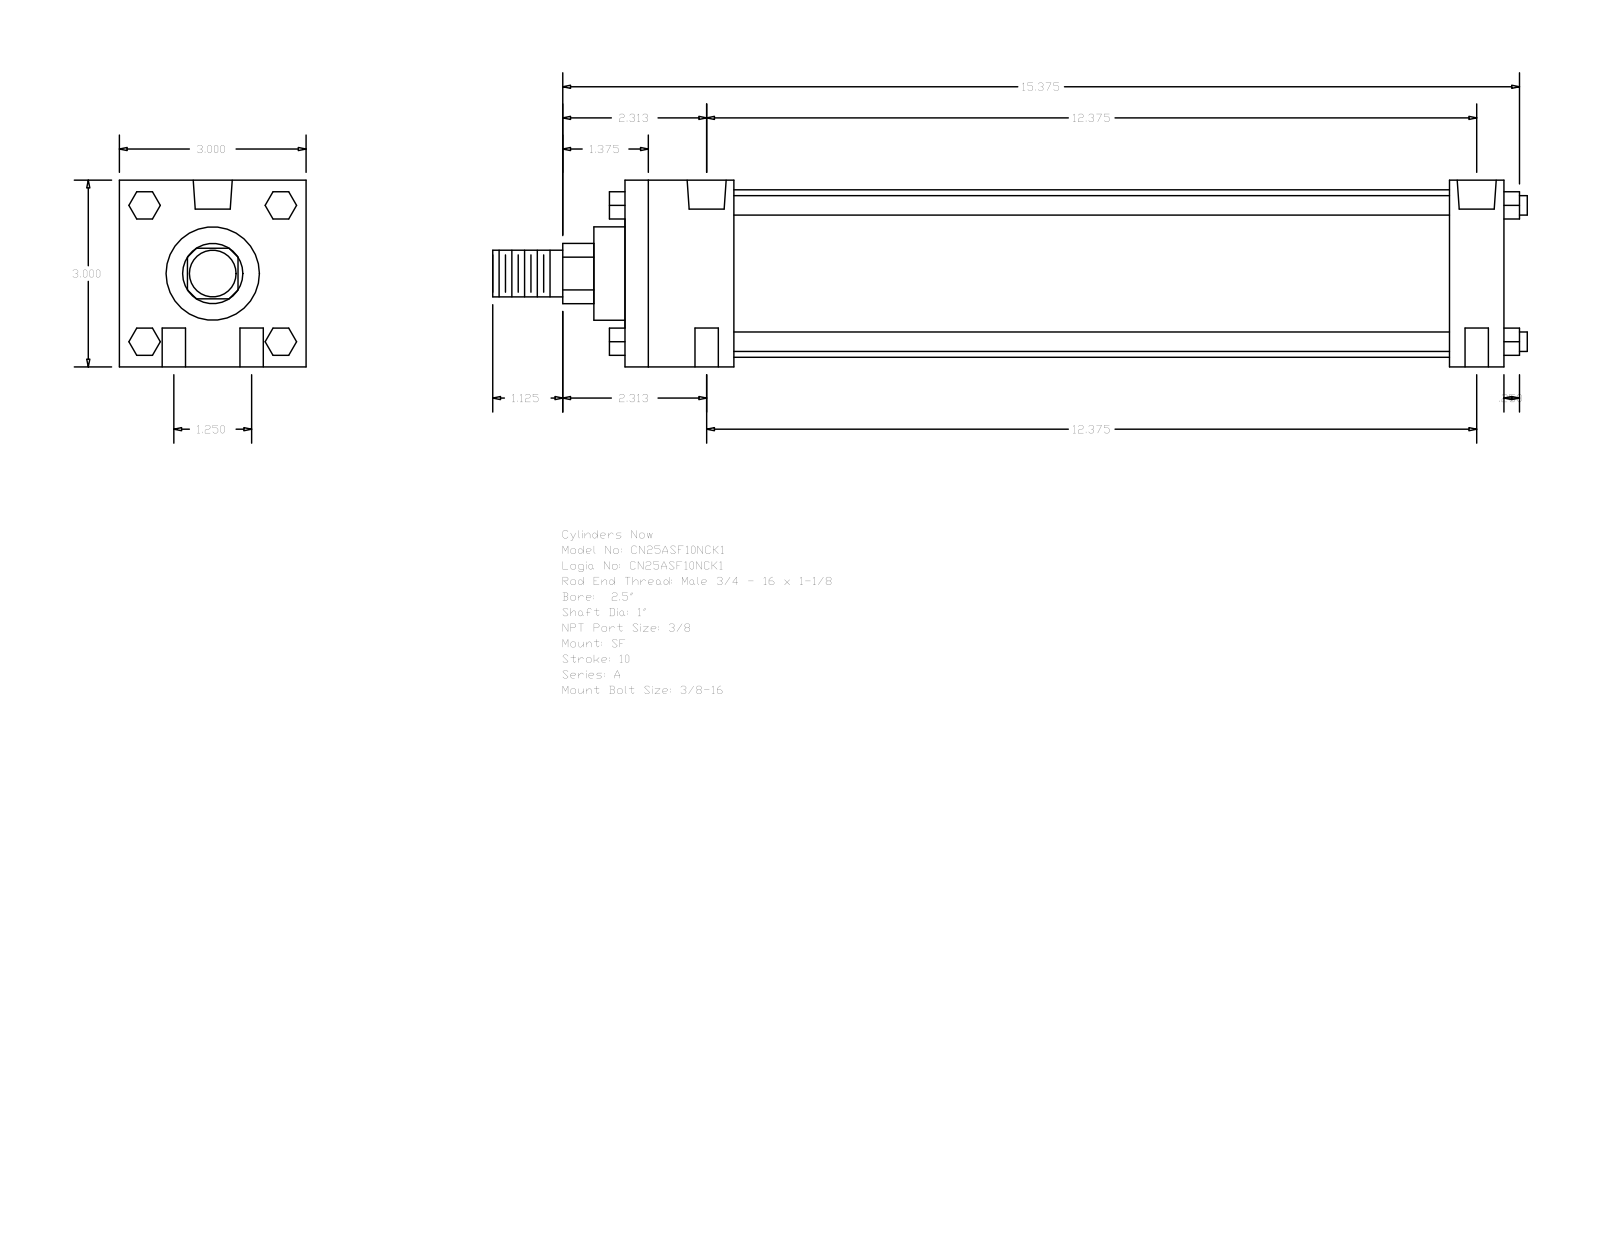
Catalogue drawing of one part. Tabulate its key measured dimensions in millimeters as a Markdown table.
| quantity | value |
| --- | --- |
| part name | A_SF__0250_1 |
| STEP written by | GSSL Pune (CONFIG_CONTROL_DESIGN) |
| units | millimeters |
| bodies | 0 solids, 124 faces (94 planar, 30 cylindrical, 0 other) |
| overall size | 422.27 × 76.2 × 76.2 |
| round holes (diameter × count) | 9.53 × 4, 5.56 × 2, 15.93 × 2 |
| round bosses / shafts (diameter × count) | 7.94 × 4, 68.33 × 1, 38.1 × 1, 25.4 × 1, 19.05 × 1 |
| partial cylindrical surfaces (radius × count) | 12.29 × 1 |
| main face-to-face distances | 76.2, 358.78, 336.55, 22.23, 44.45, 292.1, 314.33, 12.7, 11.11, 57.15 |
| hole center spacings | 15.88, 314.72, 314.32, 31.76, 315.92, 319.08 |
